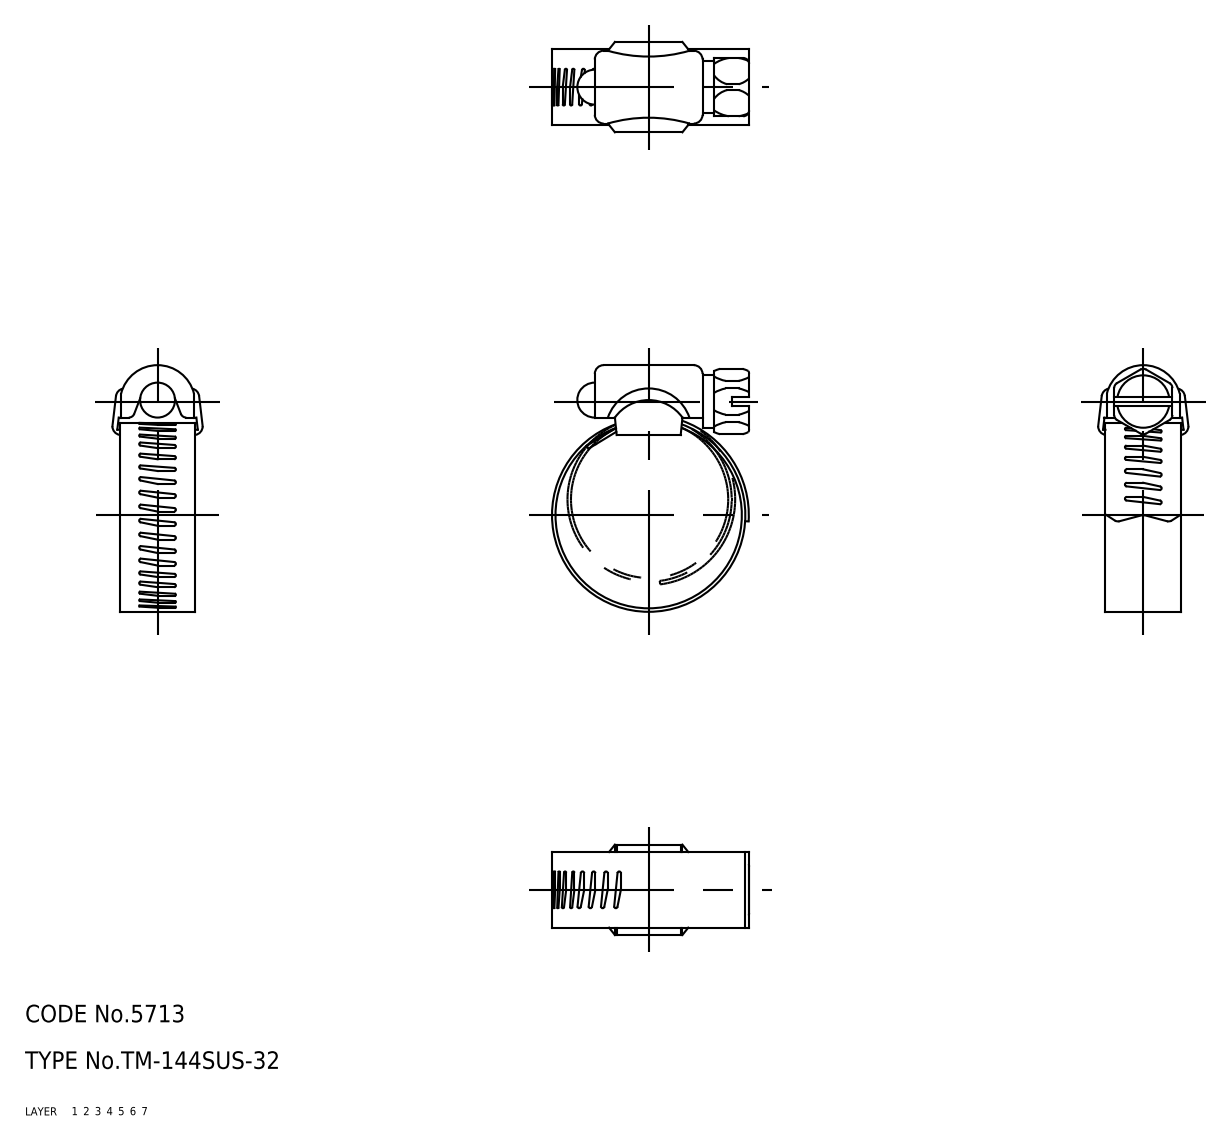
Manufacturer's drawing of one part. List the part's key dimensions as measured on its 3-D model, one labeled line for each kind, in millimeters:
Part name (STEP PRODUCT): screw; holder; band; TM_144SUS_32_20544_36
STEP written by: CADfix (AUTOMOTIVE_DESIGN)
Units: millimetres
Bodies: 3 solids, 228 faces (0 planar, 0 cylindrical, 228 other)
Overall size (bounding box): 42.45 × 33.85 × 15.63
Volume: 3 292 mm³ · Surface area: 6 017 mm²
